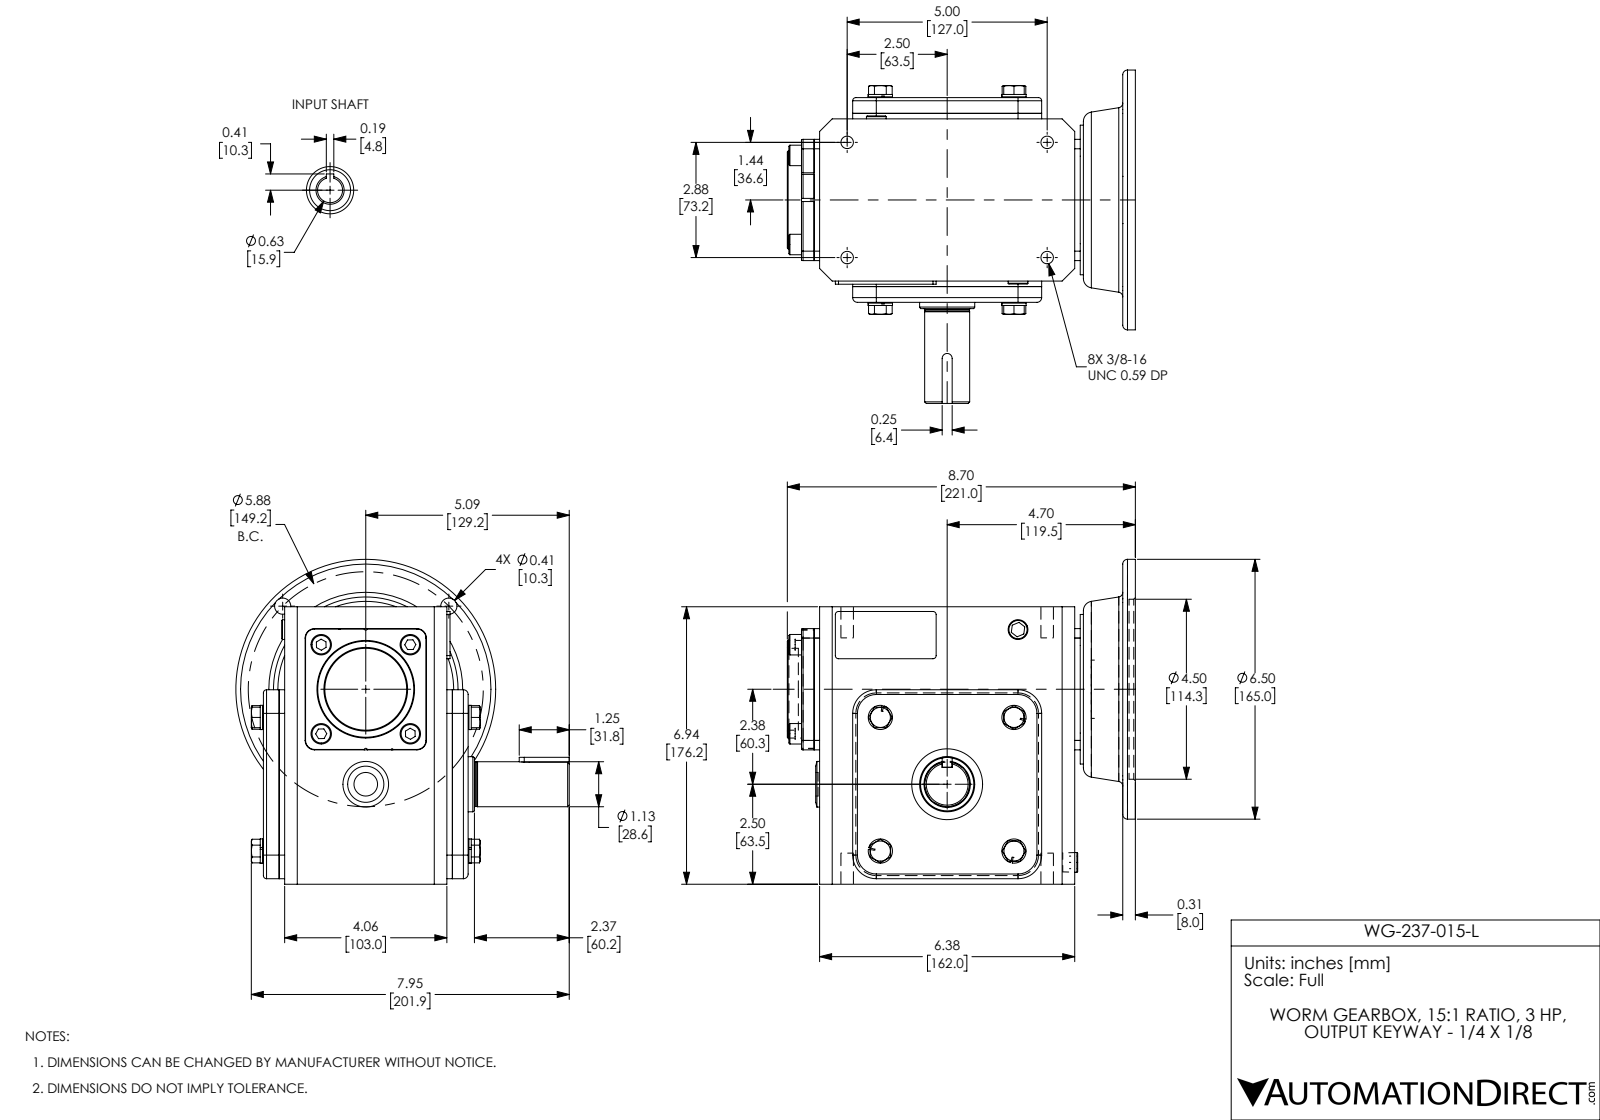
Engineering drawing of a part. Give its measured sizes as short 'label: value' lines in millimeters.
name: WG-237-015-L
written by: SolidWorks 2017 (AUTOMOTIVE_DESIGN)
unit: mm
bodies: 37 solids, 542 faces (295 planar, 157 cylindrical, 90 other)
size: 221 × 211.7 × 206.3
volume: 3 608 000 mm³; area: 331 300 mm²
holes: 4× ⌀8, 4× ⌀10.3, 1× ⌀15, 1× ⌀15.9, 1× ⌀30, 1× ⌀35, 1× ⌀37, 1× ⌀45, 1× ⌀97, 1× ⌀114.3
bosses: 4× ⌀15.4, 4× ⌀13, 1× ⌀165, 1× ⌀95, 1× ⌀62, 1× ⌀52, 1× ⌀29, 1× ⌀28.6
rounds: 12× R2, 6× R6, 4× R3, 4× R15, 2× R0.5, 2× R1, 1× R3.2
face distances: 3.5, 120, 10, 110, 13.5, 106.5, 116.5, 165.5, 176.2, 8
hole spacings: 74.6, 53.3, 73.2, 105.5, 105.5, 124.8, 127, 146.6
